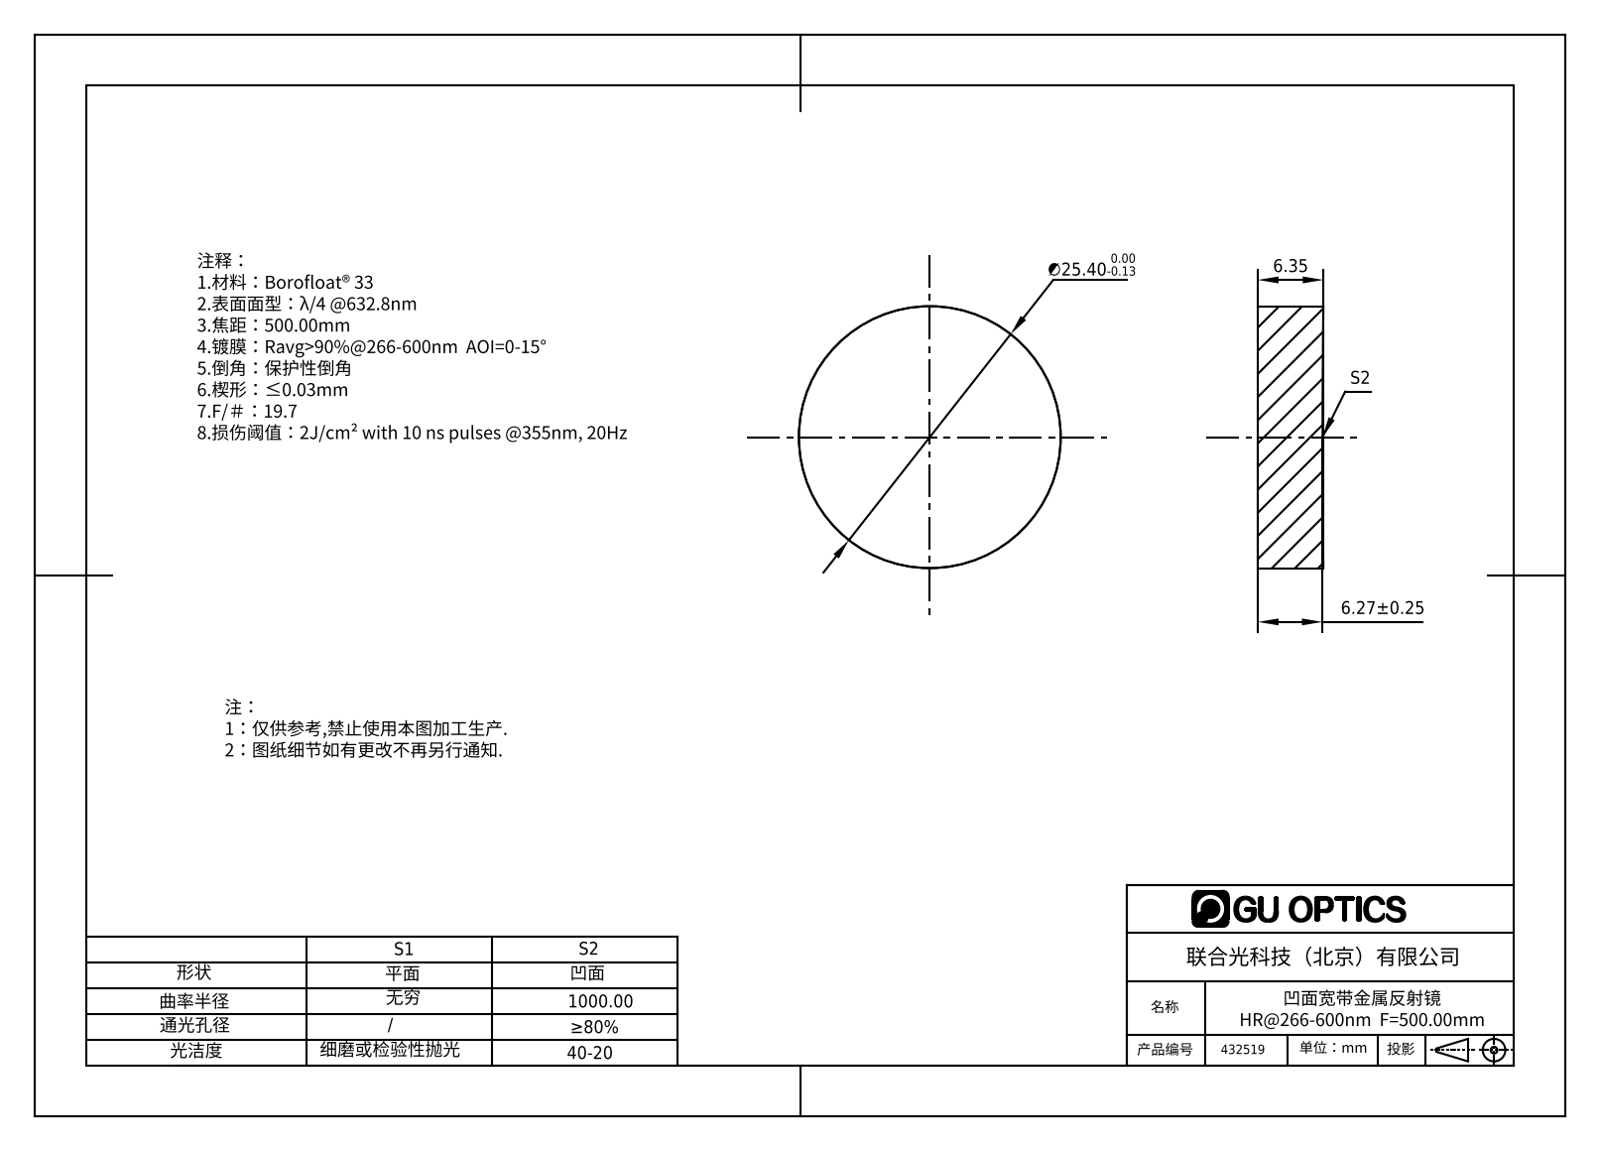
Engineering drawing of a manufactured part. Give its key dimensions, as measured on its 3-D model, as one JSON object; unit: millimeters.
{"part_name": "432519", "step_written_by": "SolidWorks 2016 (AUTOMOTIVE_DESIGN)", "units": "millimeters", "bodies": {"solids": 1, "faces": 5, "planar": 1, "cylindrical": 2, "other": 2}, "overall_size": [25.4, 25.4, 6.35], "volume_mm3": 3197, "surface_area_mm2": 1520, "round_bosses_or_shafts": [[25.4, 1]]}
